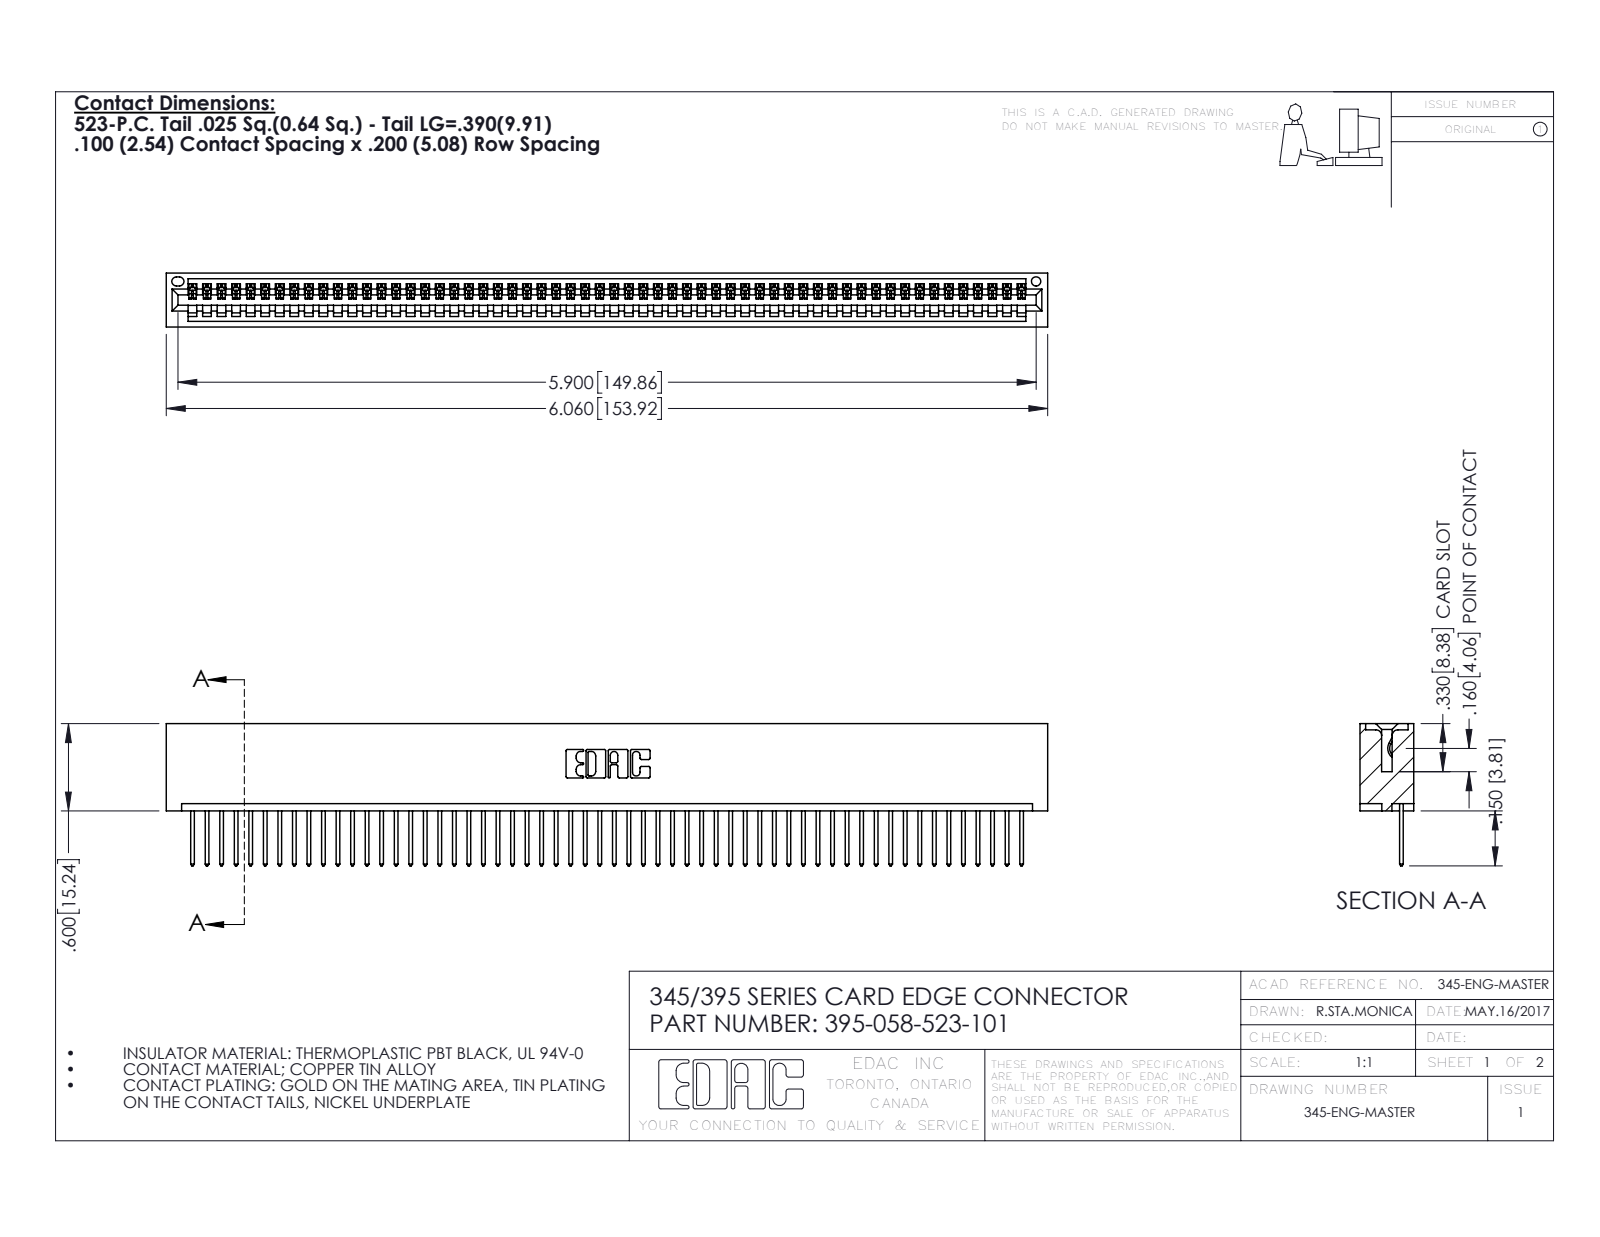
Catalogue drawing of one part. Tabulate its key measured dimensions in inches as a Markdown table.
| quantity | value |
| --- | --- |
| part name | 345-292-001_345-293-123; 345 Part_No Mounting Lugs; 395-058-523-101 |
| STEP written by | SolidWorks 2016 (CONFIG_CONTROL_DESIGN) |
| units | inches |
| bodies | 59 solids, 3482 faces (2396 planar, 1086 cylindrical, 0 other) |
| overall size | 6.06 × 0.977 × 0.37 |
| volume | 0.934 in³ |
| surface area | 32.27 in² |
| round holes (diameter × count) | 0.064 × 1 |
| partial cylindrical surfaces (radius × count) | 0.006 × 116, 0.01 × 116, 0.01 × 22, 0.007 × 6, 0.031 × 6, 0.026 × 3, 0.031 × 2, 0.04 × 2 |
| main face-to-face distances | 0.298, 0.072, 0.37, 0.2, 0.098, 0.272, 0.025, 0.225, 0.149, 0.072 |
